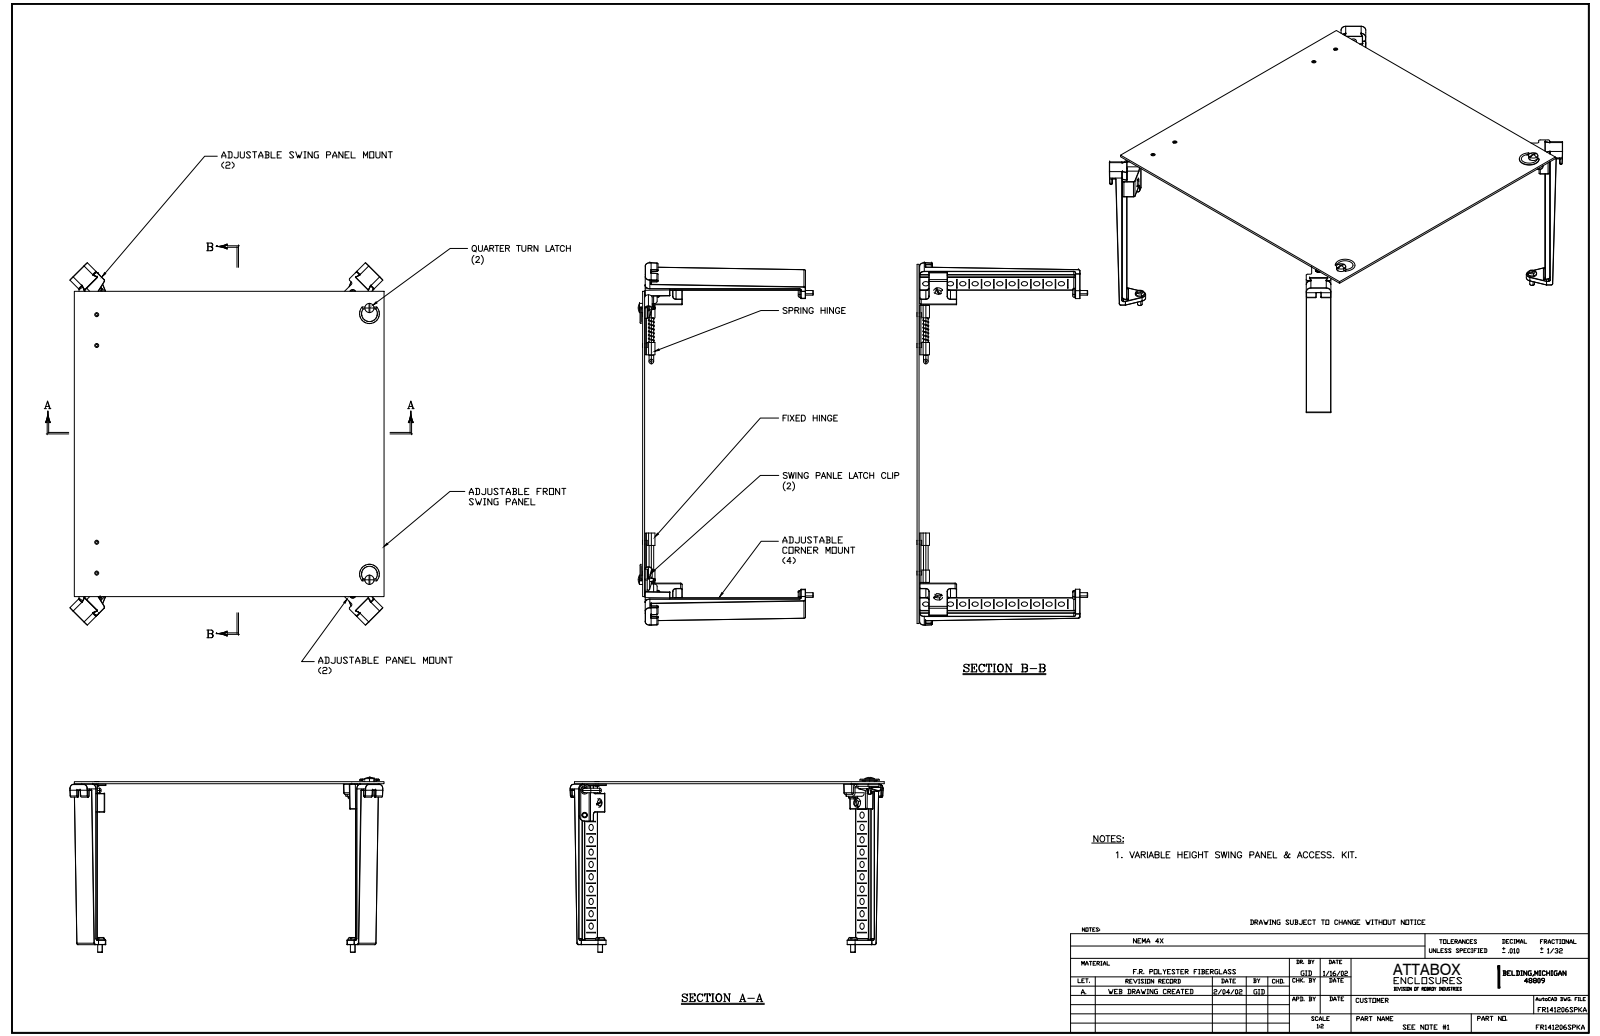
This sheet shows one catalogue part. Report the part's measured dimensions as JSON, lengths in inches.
{"part_name": "FR141208SPKA", "step_written_by": "SolidWorks 2019 (AUTOMOTIVE_DESIGN)", "units": "inches", "bodies": {"solids": 48, "faces": 2221, "planar": 1062, "cylindrical": 497, "other": 662}, "overall_size": [14.688, 12.688, 6.703], "volume_in3": 24.15, "surface_area_in2": 475.6, "round_holes": [[0.25, 52], [0.156, 6], [0.253, 6], [0.05, 4], [0.14, 4], [0.144, 4], [0.217, 4], [0.22, 4], [0.312, 3], [0.197, 2], [0.35, 2], [0.079, 1]], "round_bosses_or_shafts": [[0.19, 10], [0.373, 6], [0.246, 6], [0.433, 4], [0.315, 4], [0.16, 4], [0.079, 4], [0.394, 2]], "partial_cylinders_radius": [[0.01, 212], [0.06, 44], [0.062, 10], [0.025, 8], [0.063, 8], [0.13, 6], [0.049, 4], [0.19, 4]], "face_to_face_distances": [0.08, 16.951, 0.203, 17.154, 1, 1.414, 8.472, 8.886, 8.269, 8.683], "hole_center_spacings": [1.5, 0.5, 1, 1.732, 2.061, 2, 2.45, 2.5]}
